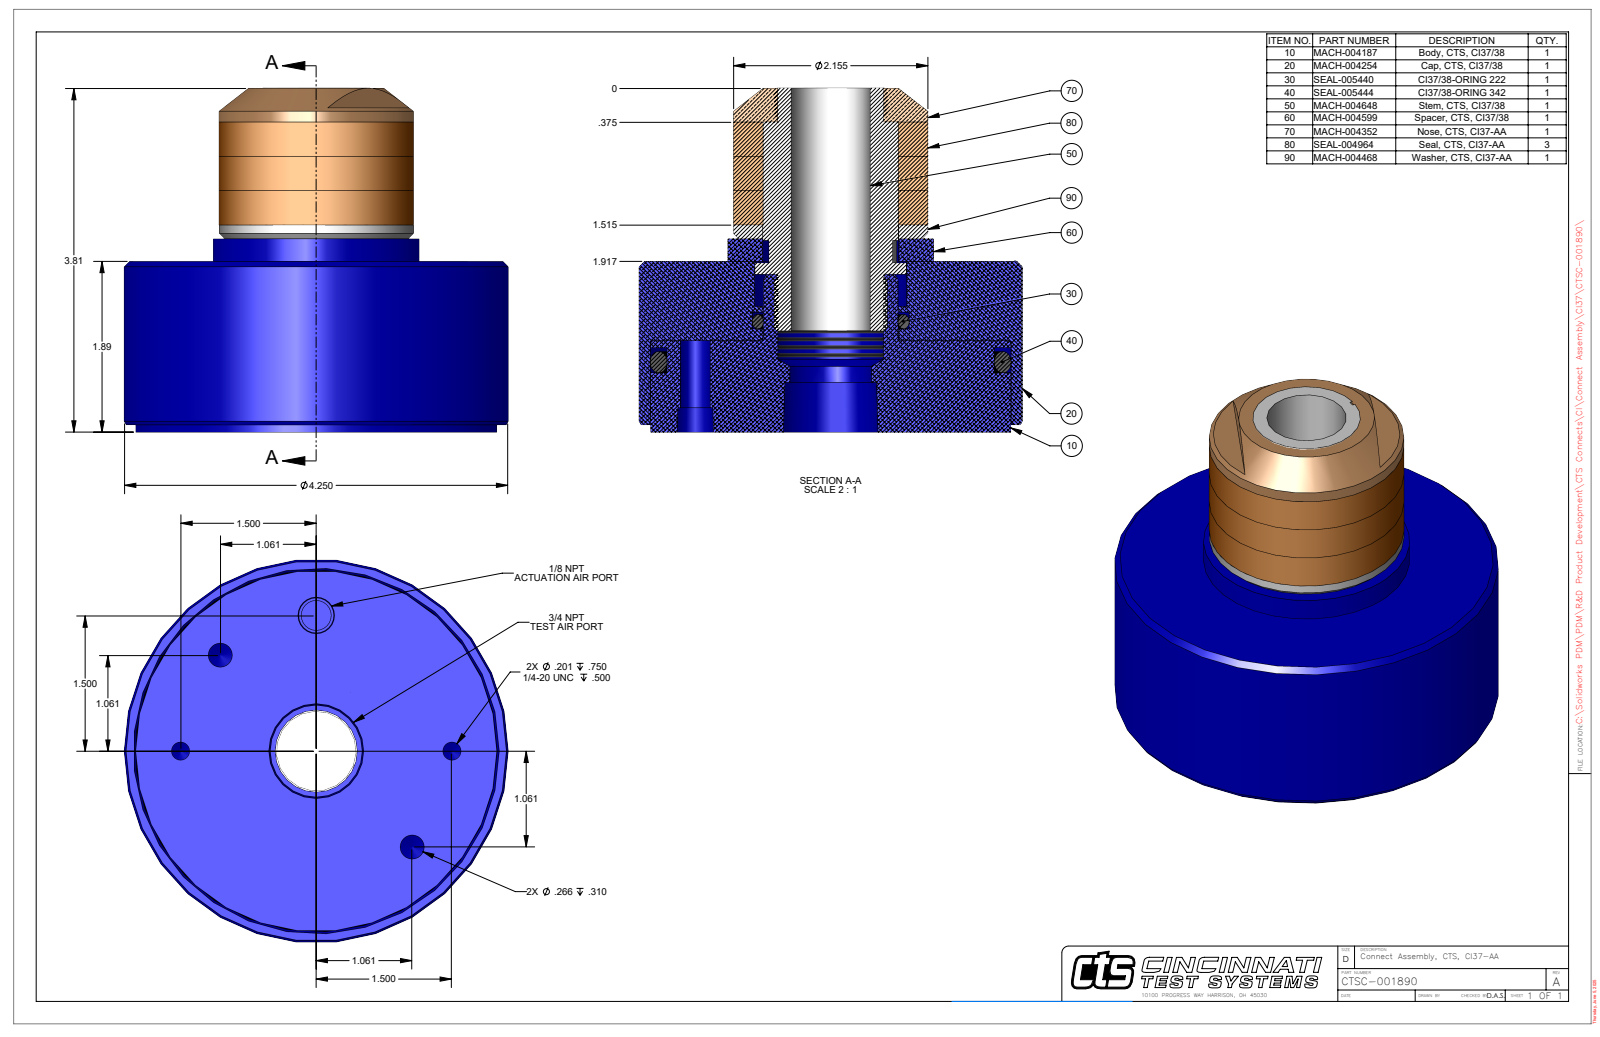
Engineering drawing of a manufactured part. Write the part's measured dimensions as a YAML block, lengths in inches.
part_name: "CTSC-001890"
step_written_by: "SolidWorks 2023 (AUTOMOTIVE_DESIGN)"
units: inches
bodies: {solids: 1, faces: 82, planar: 28, cylindrical: 31, other: 23}
overall_size: [4.25, 4.25, 3.813]
volume: 30.85
surface_area: 93.59
round_holes:
  - {diameter: 0.201, count: 2}
  - {diameter: 0.266, count: 2}
  - {diameter: 0.332, count: 1}
  - {diameter: 0.88, count: 1}
  - {diameter: 1.51, count: 1}
  - {diameter: 1.688, count: 1}
  - {diameter: 4, count: 1}
round_bosses_or_shafts:
  - {diameter: 4.25, count: 1}
  - {diameter: 3.992, count: 1}
  - {diameter: 2.281, count: 1}
  - {diameter: 2.155, count: 1}
  - {diameter: 1.674, count: 1}
  - {diameter: 1.5, count: 1}
partial_cylinders:
  - {radius: 0.586, count: 1}
face_to_face_distances: [1.893, 0.083, 1.81, 2.143, 2.06, 0.25, 3.81, 3.727, 1.917, 1.667]
hole_center_spacings: [1.5, 1.148, 2.772, 2.121, 3]
